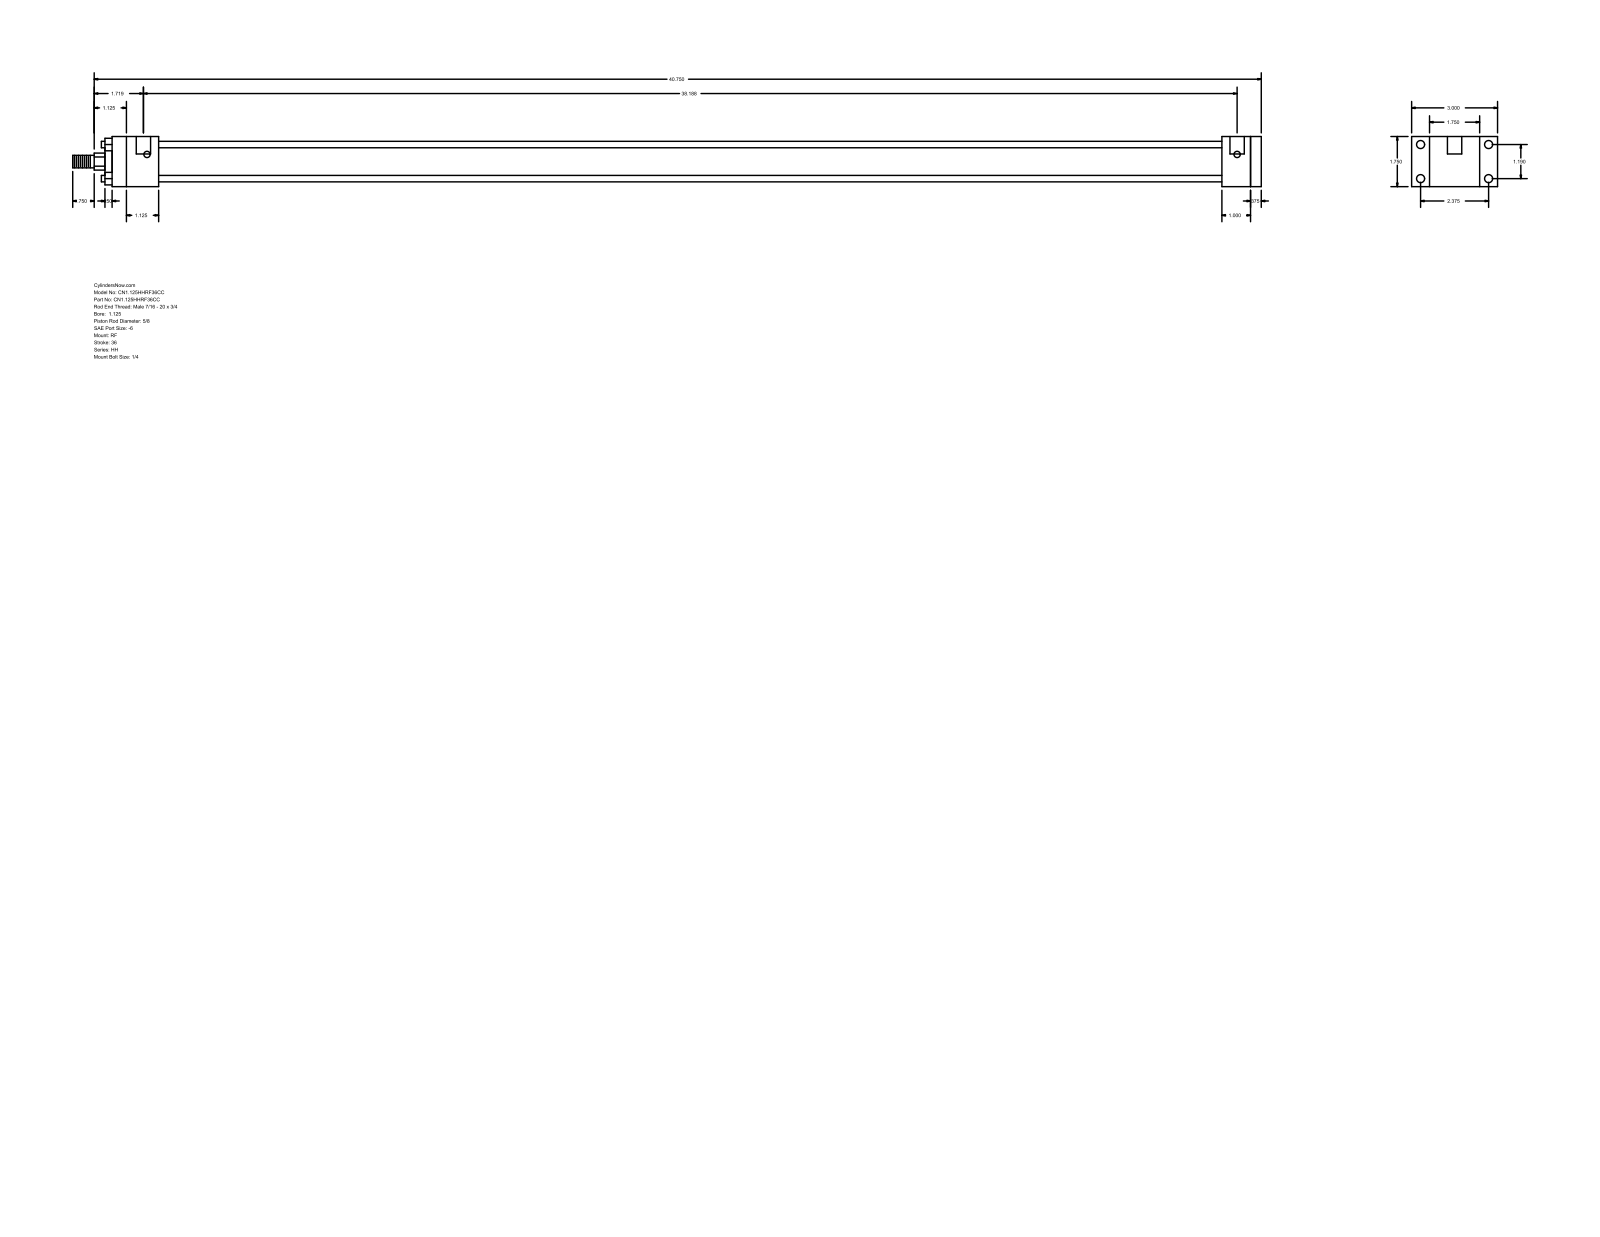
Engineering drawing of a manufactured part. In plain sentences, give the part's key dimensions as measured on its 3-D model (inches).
The part is named "HH_RF__0112_0.625". Its 3-D file was written by "GSSL Pune (CONFIG_CONTROL_DESIGN)". It is 0 solids with 92 faces: 64 planar, 28 cylindrical and 0 other. Overall it measures 41.5 by 3 by 1.75 inches. Round holes: 4 of diameter 0.219, 4 of diameter 0.281, 2 of diameter 0.5. Round bosses or shafts: 4 of diameter 0.225, 1 of diameter 1.375, 1 of diameter 1.125, 1 of diameter 0.625, 1 of diameter 0.437. Partial cylindrical surfaces (rounded edges, fillets, slot ends): 1 of radius 0.297. The main face-to-face distances are 1.75, 0.375, 1.375, 40.125, 0.625, 38.125, 38.5, 37.125, 1, 1.625. The hole center spacings are 1.19, 2.375, 2.656, 38.063, 0.125, 38.187.
